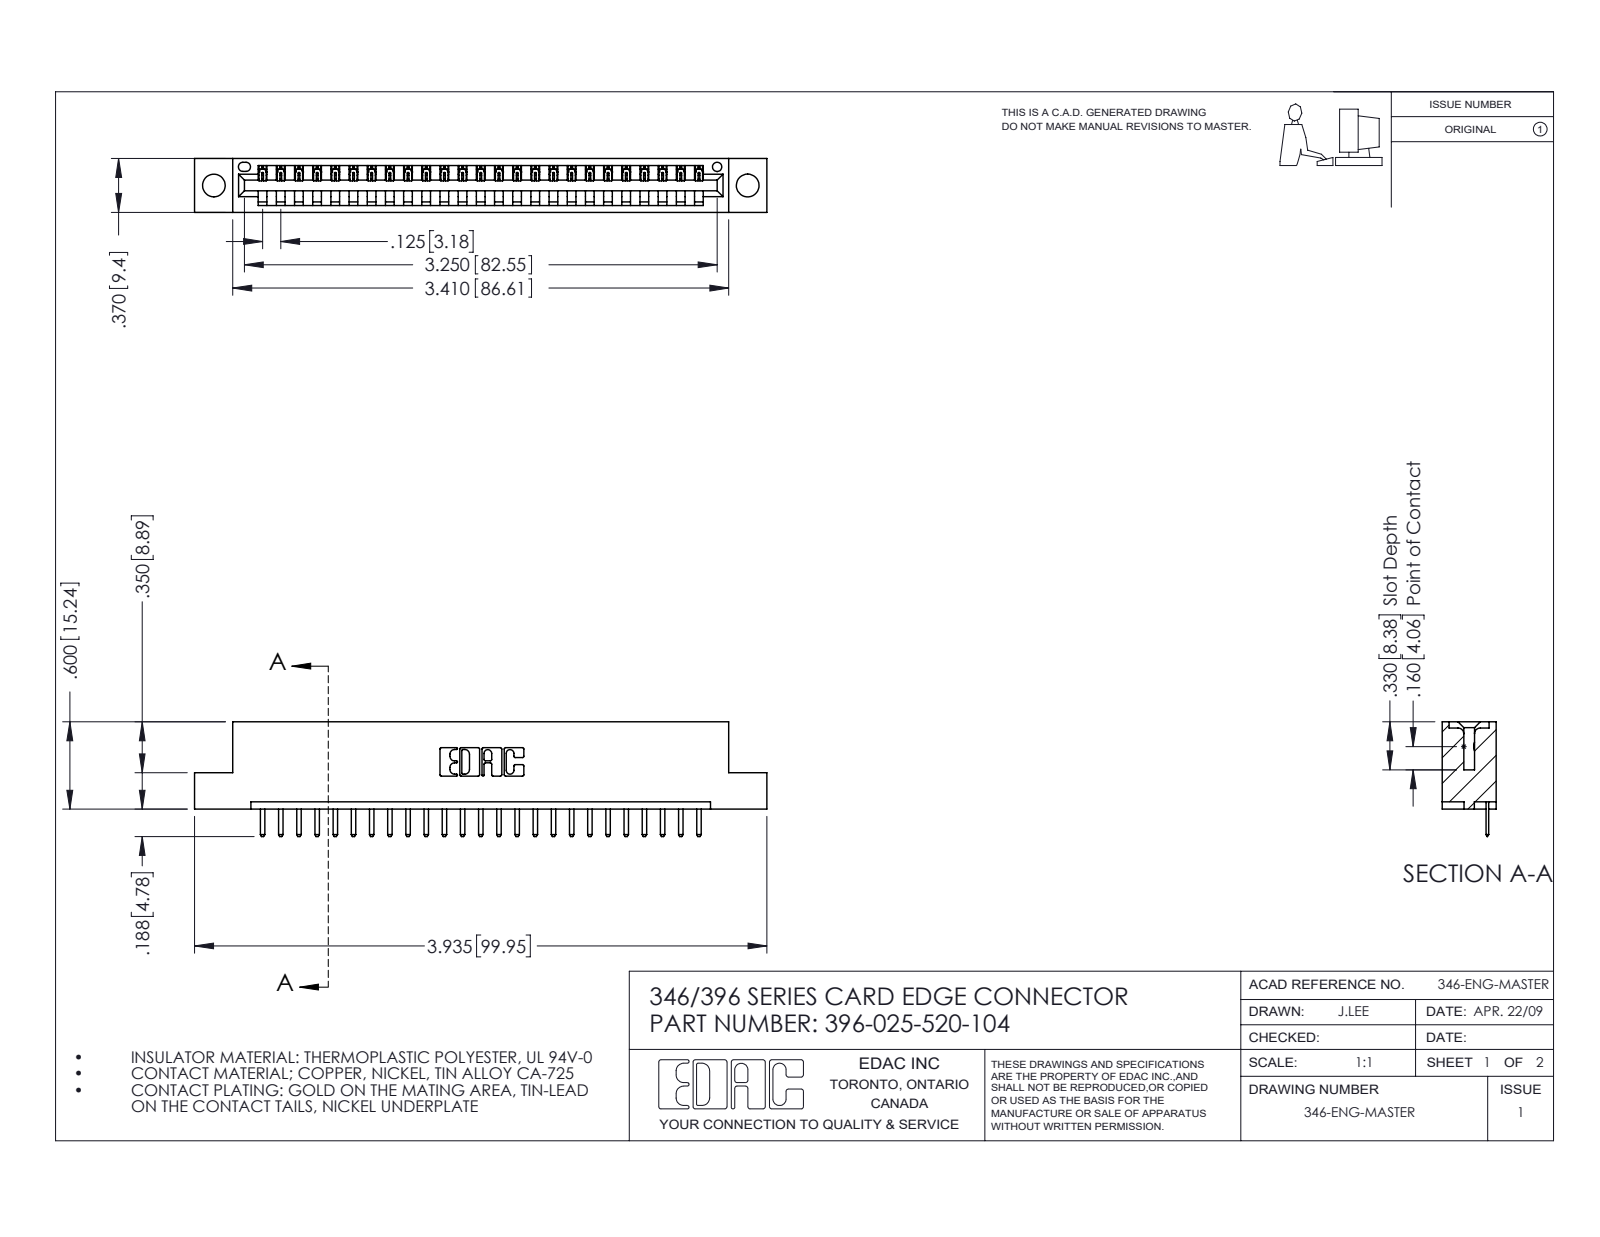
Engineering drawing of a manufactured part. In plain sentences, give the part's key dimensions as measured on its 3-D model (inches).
The part is named "396-025-520-104; 346 Part_Flush Mounting Lugs - 0.156 Dia-TH; 345-292-001_345-293-120". Its 3-D file was written by "SolidWorks 2016 (CONFIG_CONTROL_DESIGN)". It is 26 solids with 1672 faces: 1126 planar, 546 cylindrical and 0 other. Overall it measures 3.935 by 0.788 by 0.37 inches. Its volume is 0.567 cubic inches and its surface area 17.04 square inches. Round holes: 2 of diameter 0.156, 1 of diameter 0.064. Partial cylindrical surfaces (rounded edges, fillets, slot ends): 52 of radius 0.01, 50 of radius 0.006, 22 of radius 0.01, 6 of radius 0.007, 6 of radius 0.031, 3 of radius 0.026, 2 of radius 0.031, 2 of radius 0.04. The main face-to-face distances are 0.048, 0.322, 0.37, 0.25, 0.148, 0.222, 0.1, 0.174, 0.072, 0.298. The hole center spacings are 0.246, 3.462, 3.67.
